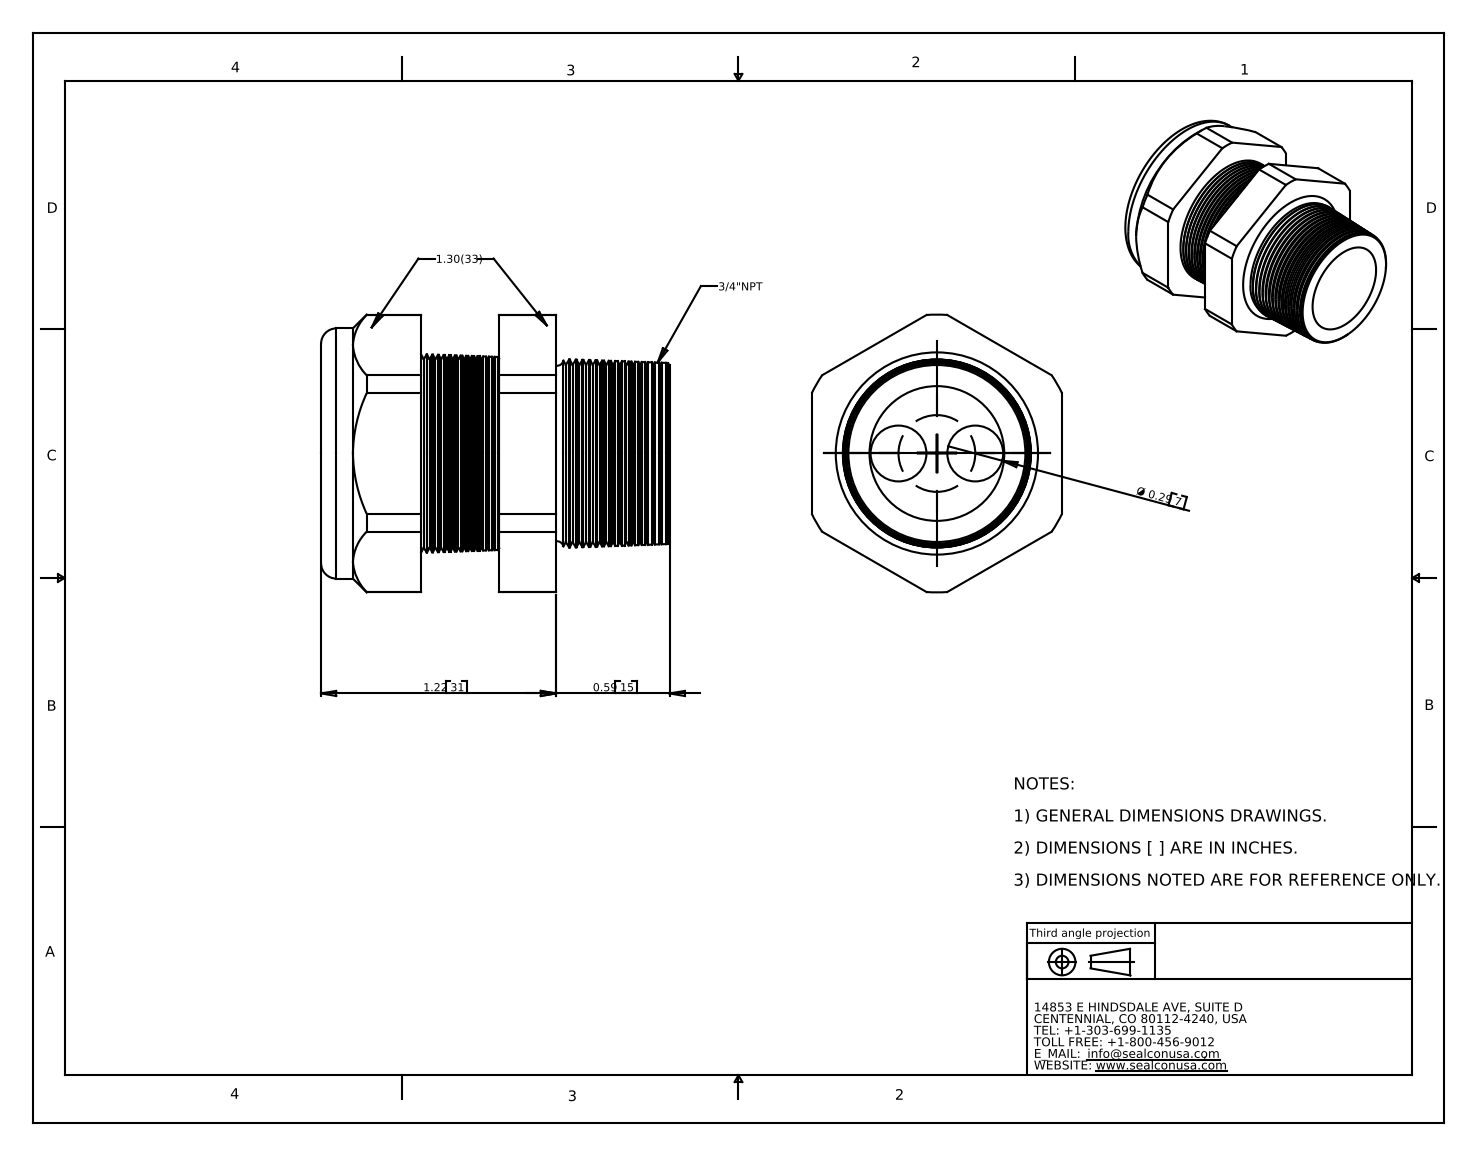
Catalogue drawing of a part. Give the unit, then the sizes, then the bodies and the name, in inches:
Units: inches
Overall size (bounding box): 1.81 × 1.443 × 1.3
Round holes (diameter × count): ⌀0.29 ×2, ⌀0.69 ×1, ⌀0.71 ×1
Round bosses / shafts (diameter × count): ⌀1.3 ×1
Partial cylindrical surfaces — rounded edges, fillets, slot ends (radius × count): R0.721 ×1
Main face-to-face distances: 1.3, 0.925, 0.52, 0.405, 1.22, 0.7, 0.295, 1.81, 1.29, 0.885
Hole centre spacings: 0.2, 0.399
Volume: 1.26 in³ · Surface area: 17.92 in²
Bodies: 2 solids, 238 faces (20 planar, 24 cylindrical, 194 other)
Part name (STEP PRODUCT): CD21N9-BK
STEP written by: SolidWorks 2007 (CONFIG_CONTROL_DESIGN)
